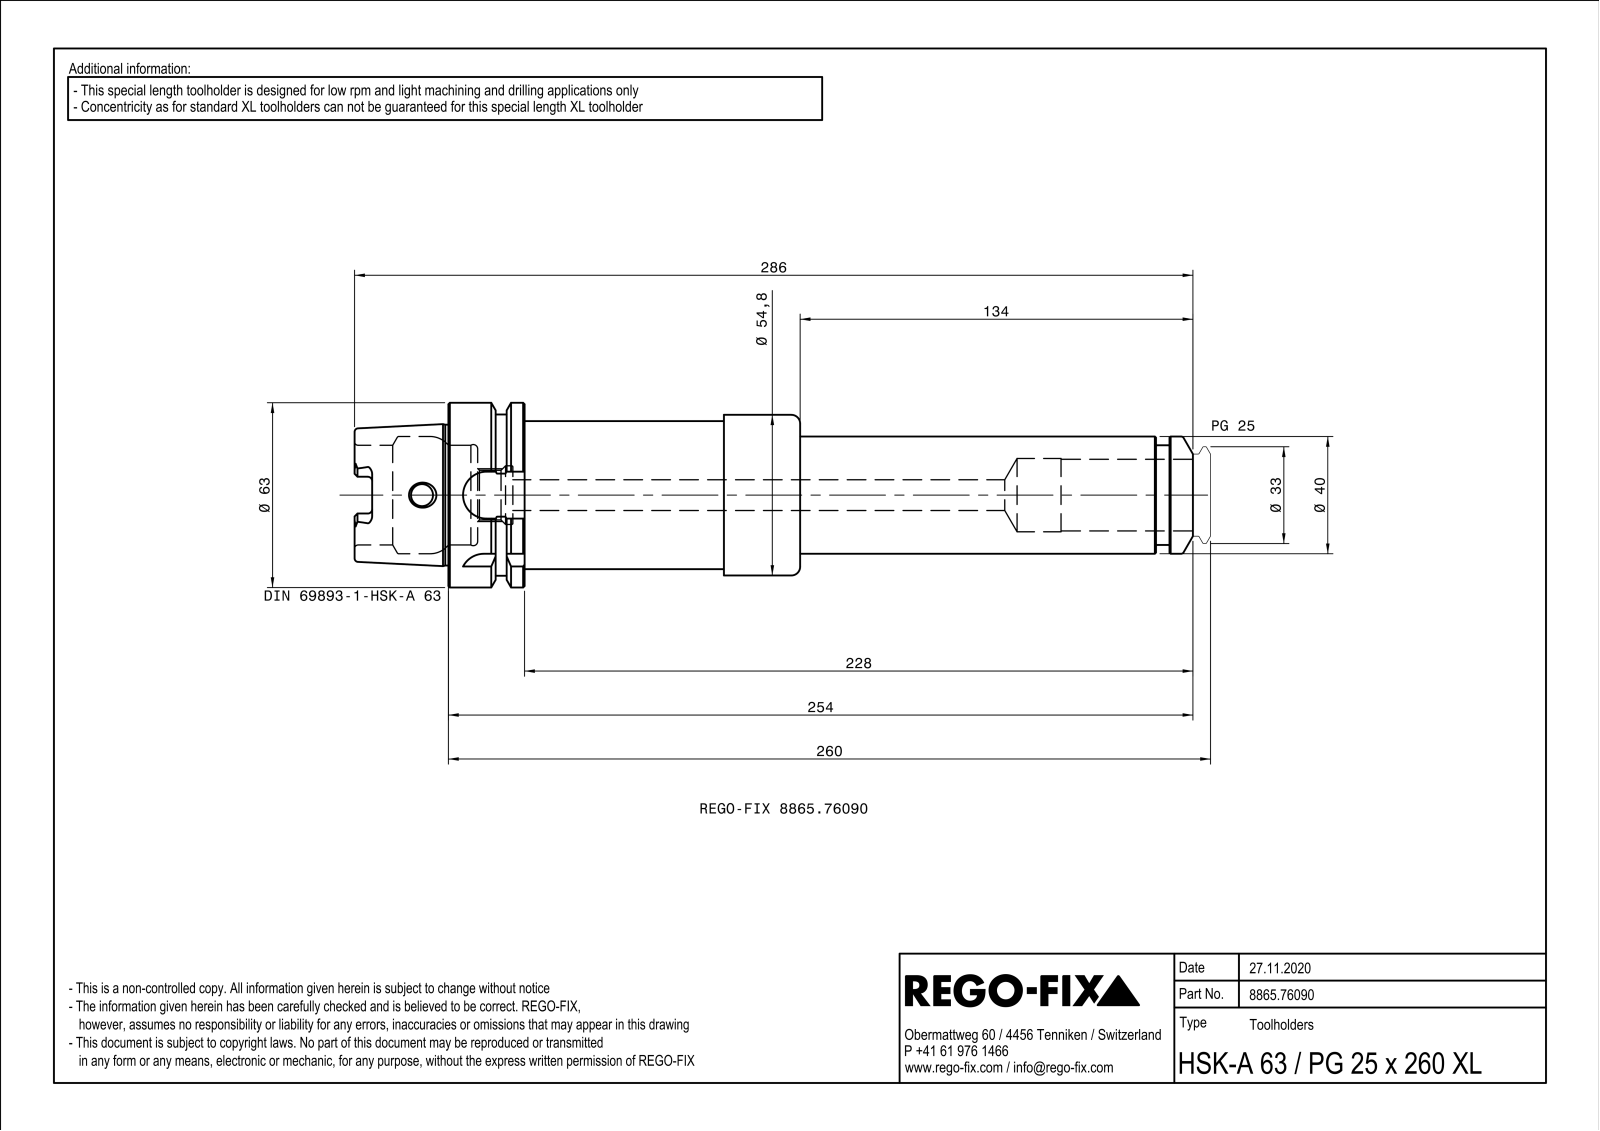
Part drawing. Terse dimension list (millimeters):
name: NOCUT
written by: SIEMENS PLM Software Solid Edge ST10 (AUTOMOTIVE_DESIGN)
unit: mm
bodies: 1 solid, 198 faces (60 planar, 53 cylindrical, 85 other)
size: 286 × 63 × 63
volume: 379 806 mm³; area: 78 193 mm²
holes: 1× ⌀7.5, 1× ⌀8.4, 1× ⌀9, 1× ⌀10, 1× ⌀12, 1× ⌀14, 1× ⌀16.92, 1× ⌀20, 1× ⌀25, 1× ⌀33, 1× ⌀34, 1× ⌀40.2
bosses: 1× ⌀63, 1× ⌀55, 1× ⌀54.8, 1× ⌀50.5, 1× ⌀50, 1× ⌀49.3, 1× ⌀48.04, 1× ⌀45
rounds: 6× R1.5, 4× R2.88, 4× R8, 1× R27.35
face distances: 26, 94, 120, 8, 10, 152, 126, 16, 86, 112
